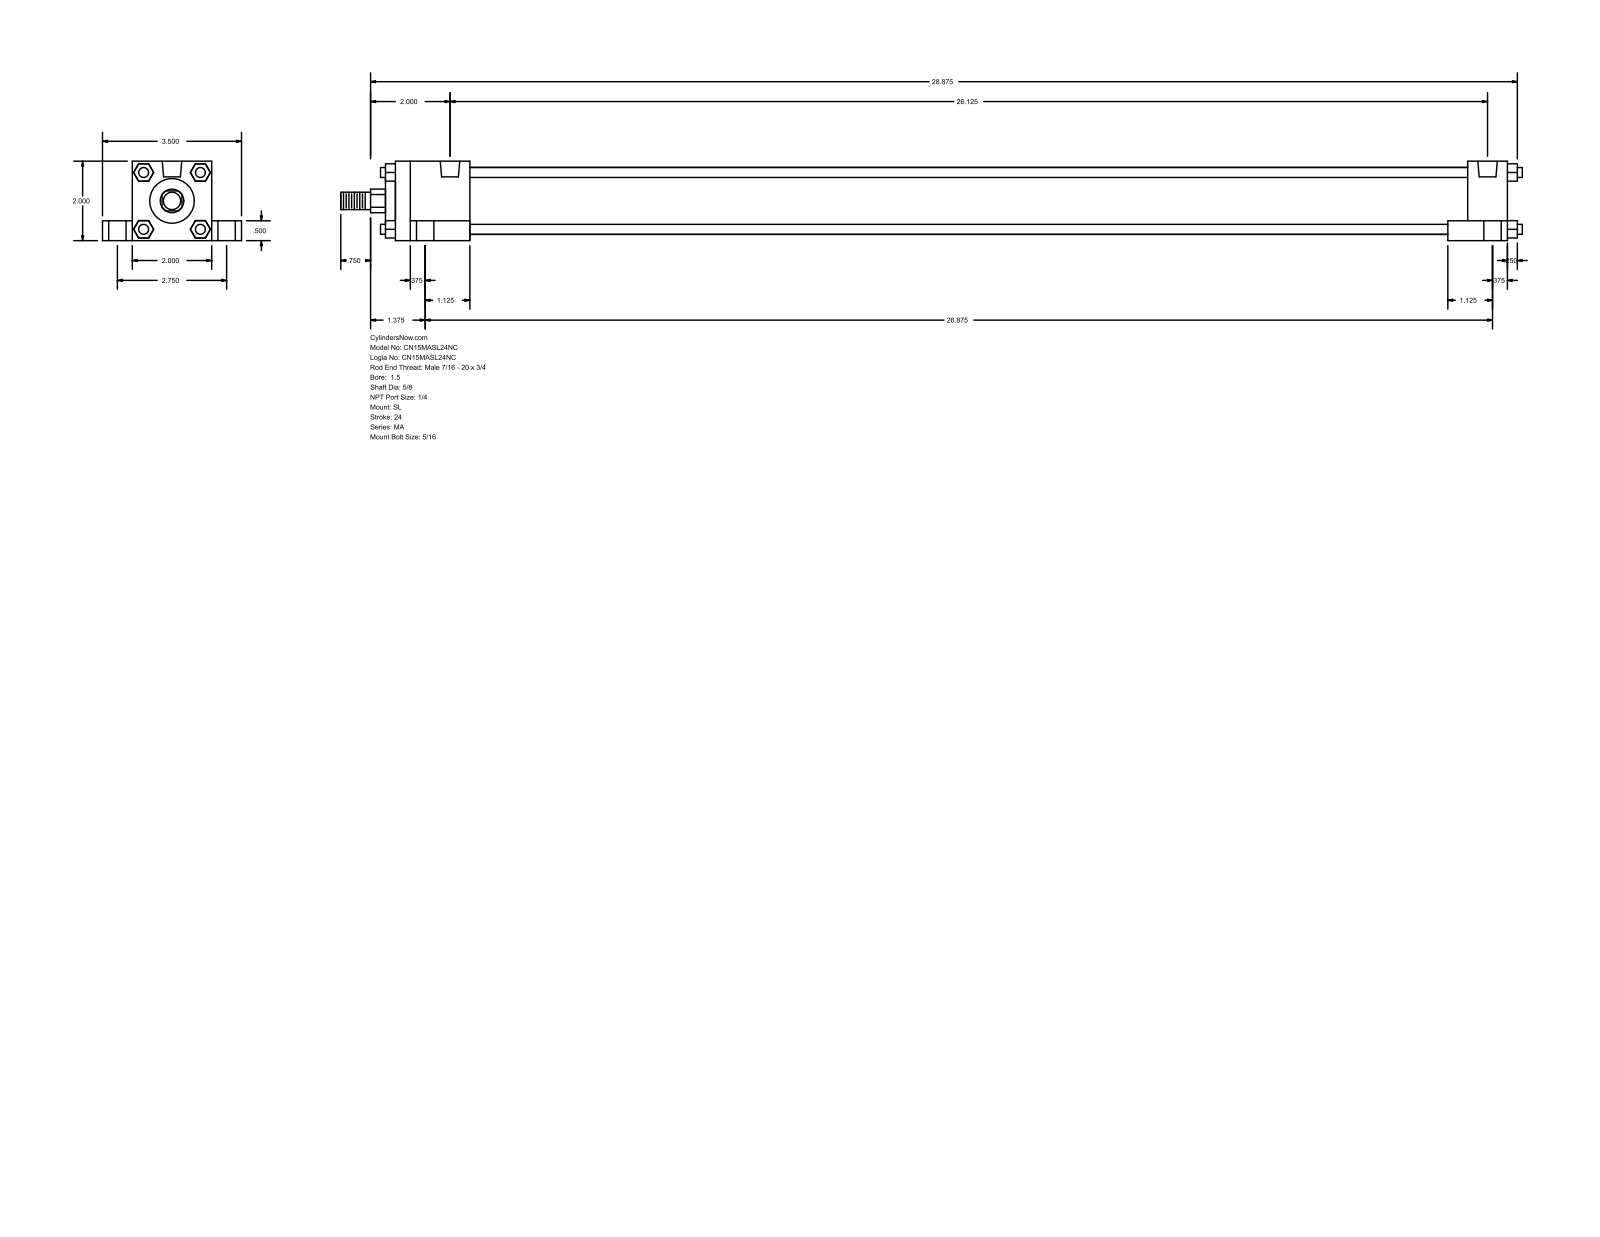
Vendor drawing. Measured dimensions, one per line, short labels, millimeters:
name: MA_SL__0150_0.625
written by: GSSL Pune (CONFIG_CONTROL_DESIGN)
unit: mm
bodies: 0 solids, 148 faces (112 planar, 36 cylindrical, 0 other)
size: 755.65 × 88.9 × 50.8
holes: 4× ⌀7.94, 4× ⌀11.11, 4× ⌀17.46, 2× ⌀12.49
bosses: 4× ⌀6.35, 1× ⌀42.93, 1× ⌀28.57, 1× ⌀15.88, 1× ⌀11.11
rounds: 1× R7.54
face distances: 50.8, 19.05, 38.1, 711.2, 69.85, 12.7, 638.17, 9.52, 685.79, 25.41
hole spacings: 35.06, 38.36, 69.84, 663.58, 667.66, 680.36, 682.63, 686.19
